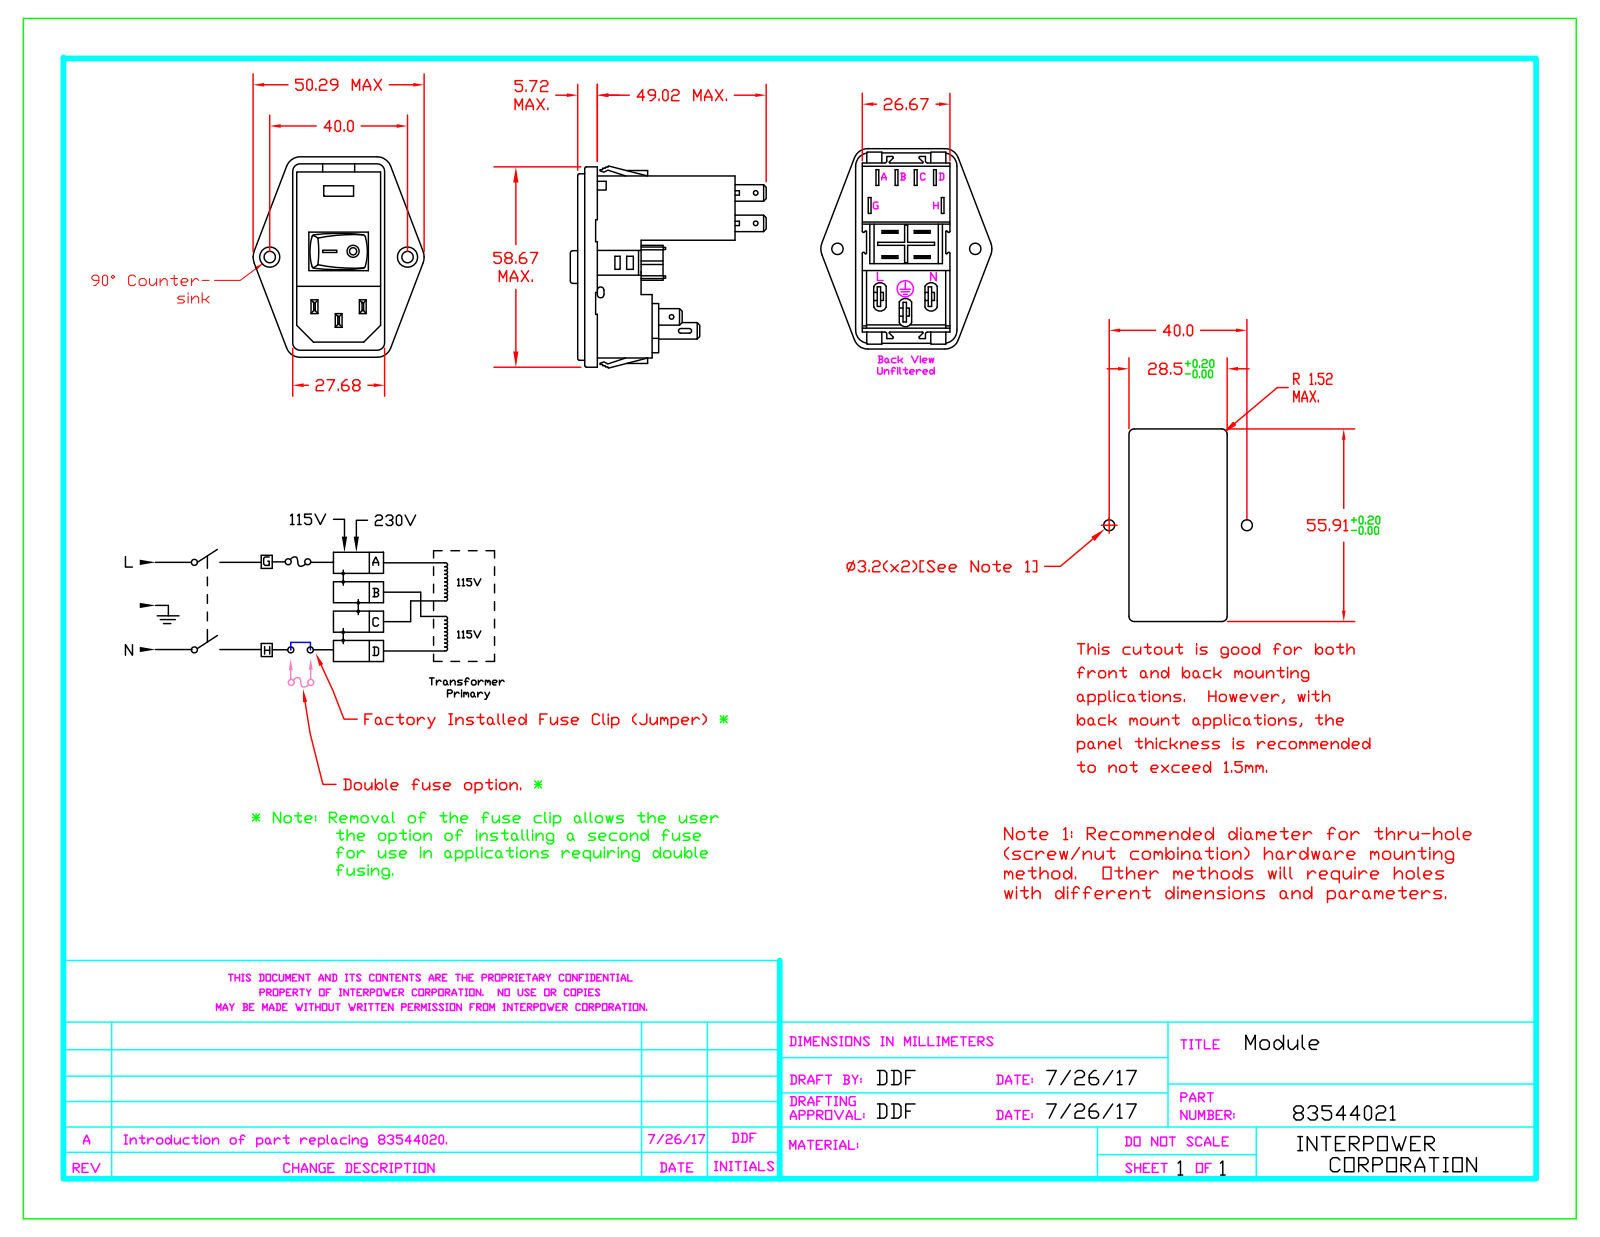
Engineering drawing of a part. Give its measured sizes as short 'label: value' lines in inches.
name: 83544020
written by: SolidWorks 2007 (CONFIG_CONTROL_DESIGN)
unit: in
bodies: 1 solid, 656 faces (491 planar, 92 cylindrical, 73 other)
size: 2.343 × 2.233 × 1.98
volume: 2.277 in³; area: 26.84 in²
holes: 5× ⌀0.052, 2× ⌀0.114, 1× ⌀0.089, 1× ⌀0.138
bosses: 1× ⌀0.113, 1× ⌀0.108
rounds: 19× R0.039, 10× R0.02, 5× R0.01, 4× R0.085, 4× R0.165, 2× R0.026, 2× R0.03, 2× R0.197
face distances: 1.024, 0.734, 0.145, 0.225, 0.08, 0.019, 0.5, 0.64, 1.573, 1.718
hole spacings: 1.243, 0.347, 0.417, 1.436, 1.575, 1.71
